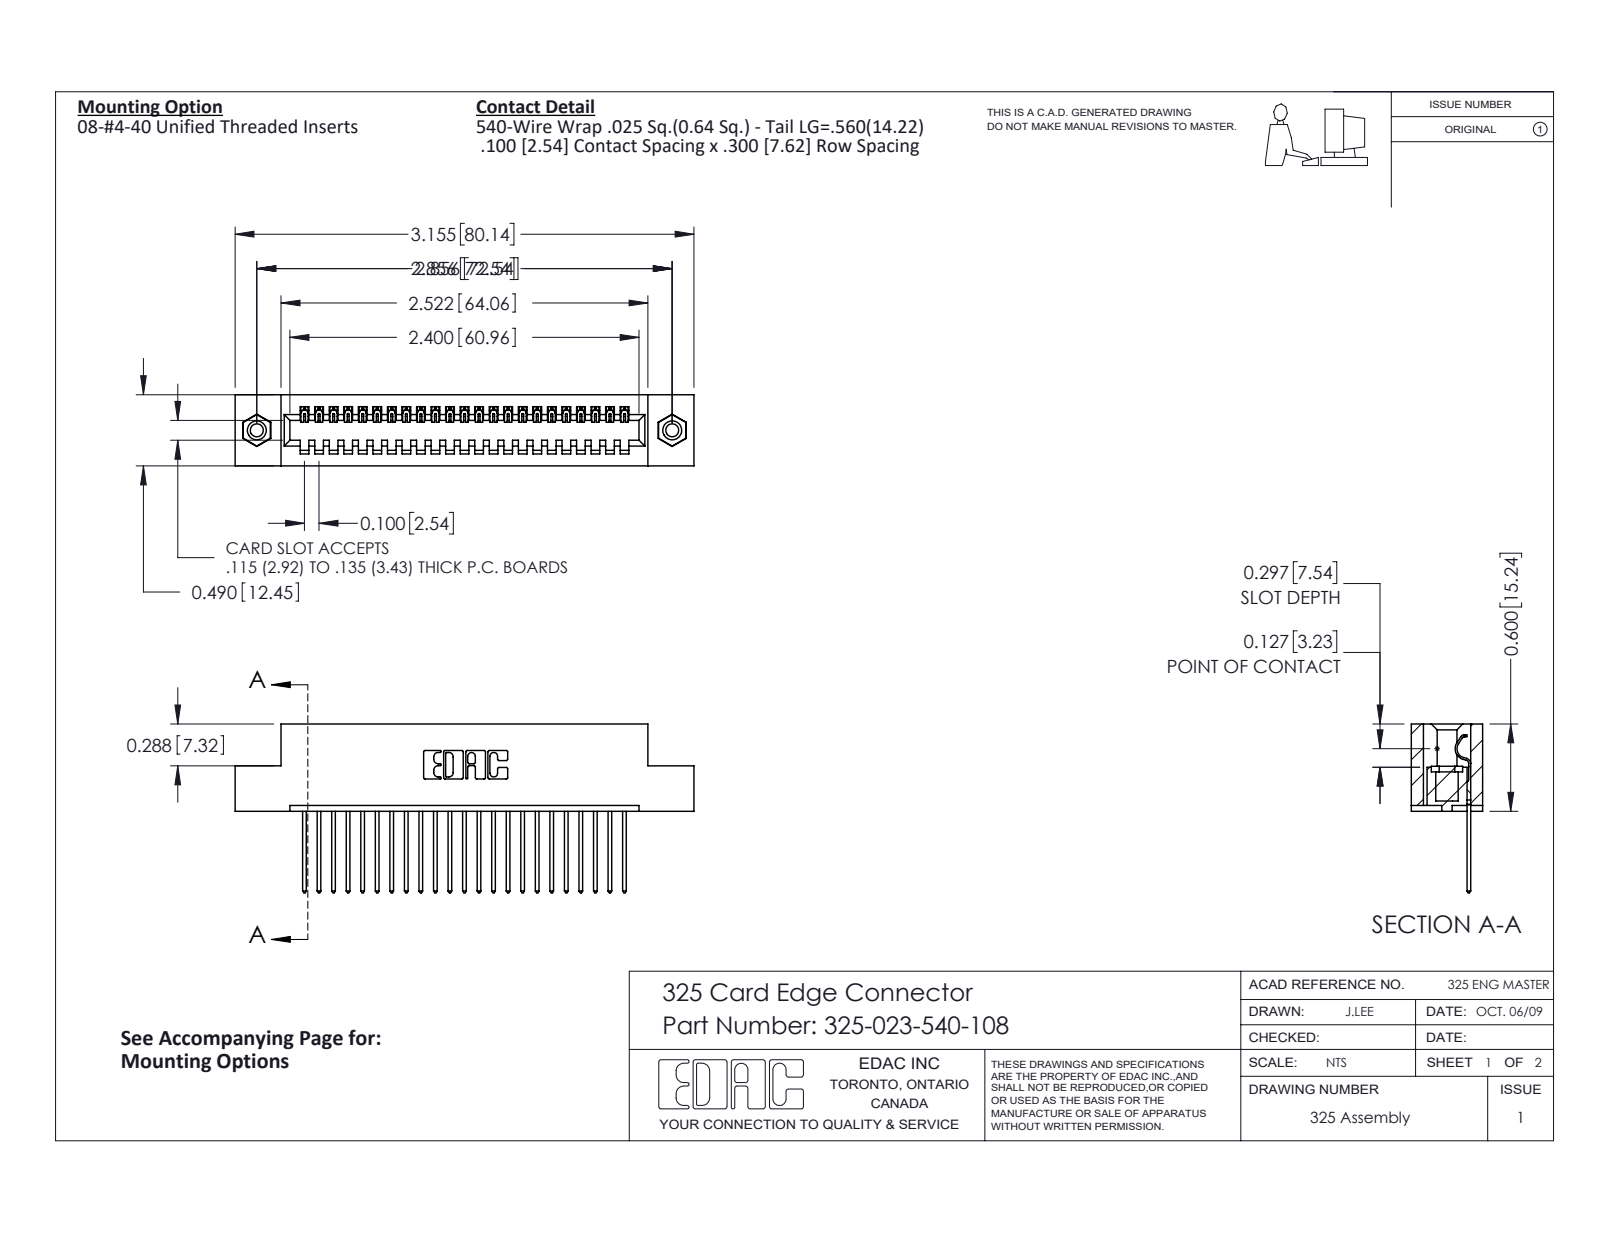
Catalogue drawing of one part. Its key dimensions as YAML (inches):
part_name: "345-250-001_345-250-003-102; 325-023-540-108; 325-292-001_325-293-140; 325 Part_TI"
step_written_by: "SolidWorks 2016 (CONFIG_CONTROL_DESIGN)"
units: inches
bodies: {solids: 26, faces: 1508, planar: 1068, cylindrical: 424, other: 16}
overall_size: [3.155, 1.16, 0.49]
volume: 0.613
surface_area: 16.9
round_holes:
  - {diameter: 0.089, count: 2}
  - {diameter: 0.125, count: 2}
  - {diameter: 0.16, count: 2}
round_bosses_or_shafts:
  - {diameter: 0.155, count: 2}
partial_cylinders:
  - {radius: 0.006, count: 46}
  - {radius: 0.01, count: 46}
  - {radius: 0.01, count: 22}
  - {radius: 0.007, count: 6}
  - {radius: 0.031, count: 6}
  - {radius: 0.026, count: 3}
  - {radius: 0.014, count: 1}
  - {radius: 0.022, count: 1}
face_to_face_distances: [0.083, 0.407, 0.49, 0.3, 0.107, 0.383, 0.025, 0.04, 0.325, 0.6]
hole_center_spacings: [2.856]
